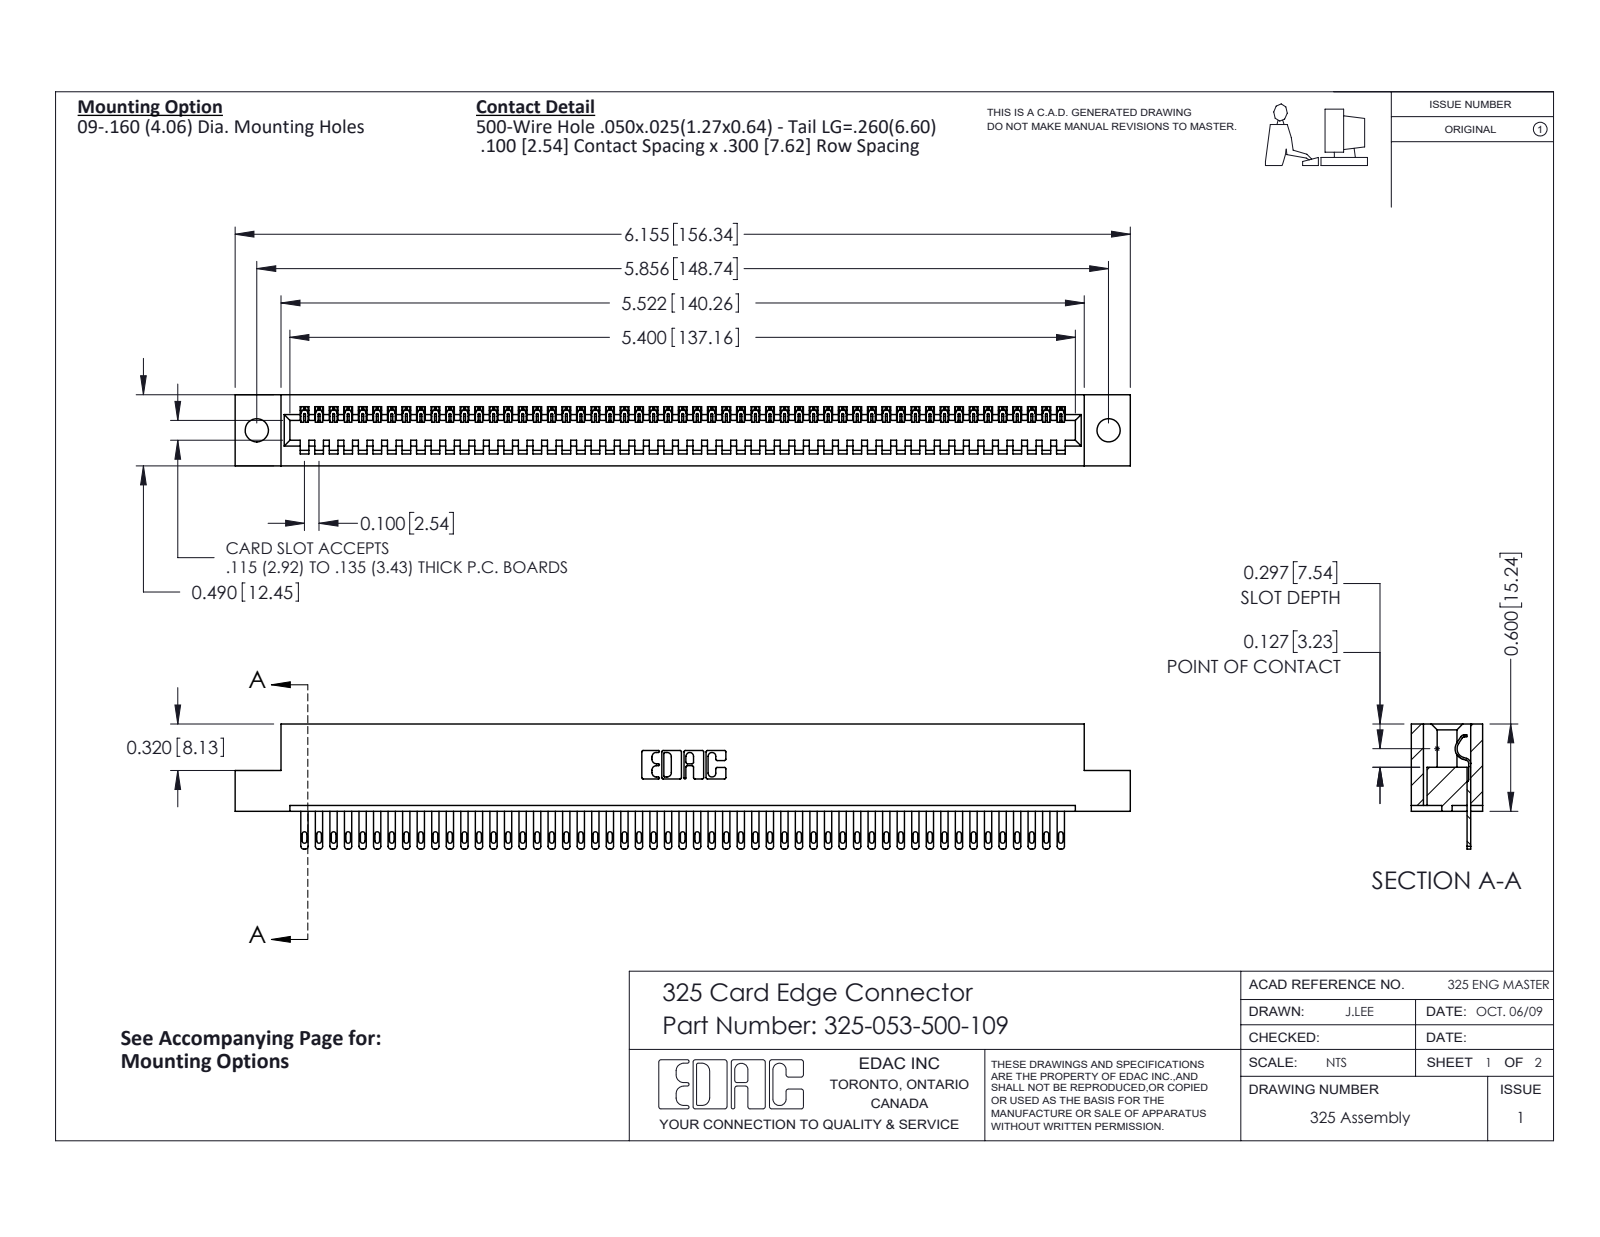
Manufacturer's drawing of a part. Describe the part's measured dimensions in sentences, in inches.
The part is named "325-292-001_325-293-100; 325-053-500-109; 325 Part_.160 TH". Its 3-D file was written by "SolidWorks 2016 (CONFIG_CONTROL_DESIGN)". It is 54 solids with 2976 faces: 1978 planar, 998 cylindrical and 0 other. Overall it measures 6.155 by 0.86 by 0.49 inches. Its volume is 1.204 cubic inches and its surface area 33.74 square inches. Round holes: 2 of diameter 0.16. Partial cylindrical surfaces (rounded edges, fillets, slot ends): 106 of radius 0.006, 106 of radius 0.016, 106 of radius 0.02, 22 of radius 0.01, 6 of radius 0.007, 6 of radius 0.031, 3 of radius 0.026, 1 of radius 0.014. The main face-to-face distances are 0.083, 0.407, 0.49, 0.3, 0.107, 0.383, 0.025, 0.325, 0.263, 0.56. The hole center spacings are 5.856.
